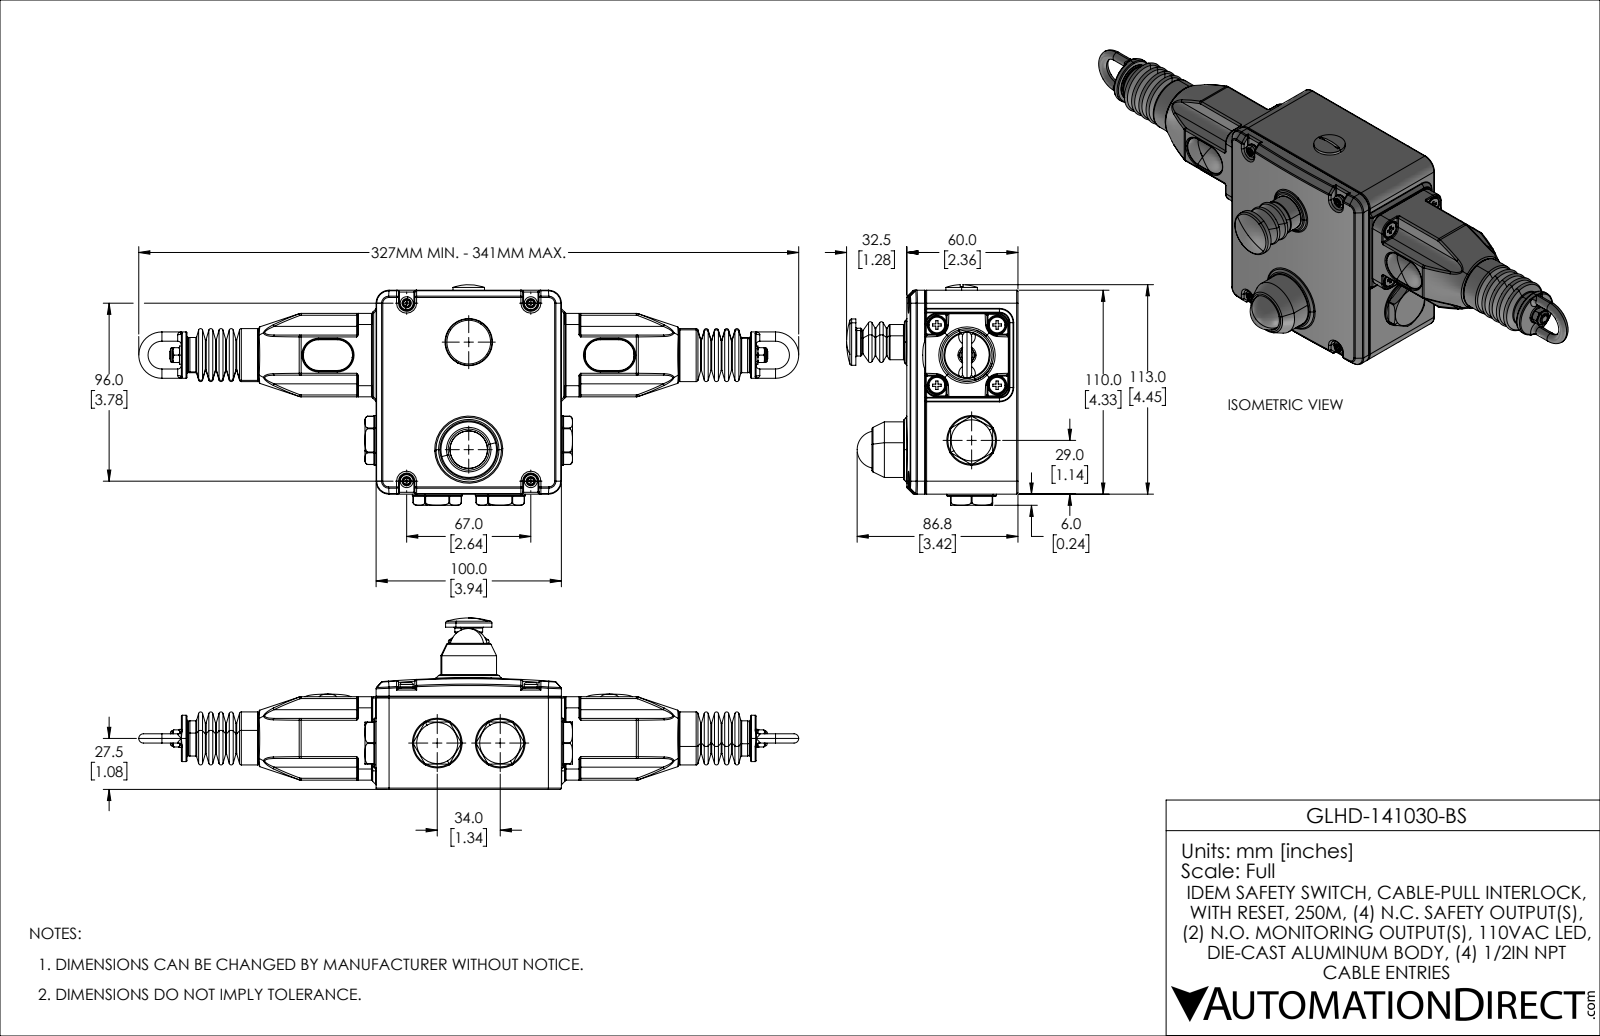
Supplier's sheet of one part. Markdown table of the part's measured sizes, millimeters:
| quantity | value |
| --- | --- |
| part name | GLHD-141030-AS |
| STEP written by | SolidWorks 2021 (AUTOMOTIVE_DESIGN) |
| units | millimeters |
| bodies | 48 solids, 5222 faces (1454 planar, 1737 cylindrical, 2031 other) |
| overall size | 356.2 × 119 × 92.5 |
| volume | 349 400 mm³ |
| surface area | 221 600 mm² |
| round holes (diameter × count) | 5 × 10, 5.3 × 5, 9 × 5, 2.4 × 4, 3.3 × 4, 4 × 4, 4.8 × 4, 5.4 × 4, 5.8 × 4, 9.5 × 4, 1.7 × 3, 2.6 × 3 |
| round bosses / shafts (diameter × count) | 6 × 7, 7 × 5, 8.5 × 4, 4.4 × 4, 3.5 × 4, 1.3 × 4, 26.8 × 3, 19.4 × 3 |
| partial cylindrical surfaces (radius × count) | 0.5 × 287, 1 × 142, 0.7 × 80, 0.2 × 76, 0.3 × 32, 0.1 × 14, 0.2 × 14, 5 × 12 |
| main face-to-face distances | 3.5, 54.8, 2.9, 51.9, 110, 45, 98.5, 4, 2, 11.7 |
| hole center spacings | 5.8, 9.5, 23, 32.5, 48, 48.6, 76.5, 88.6 |
